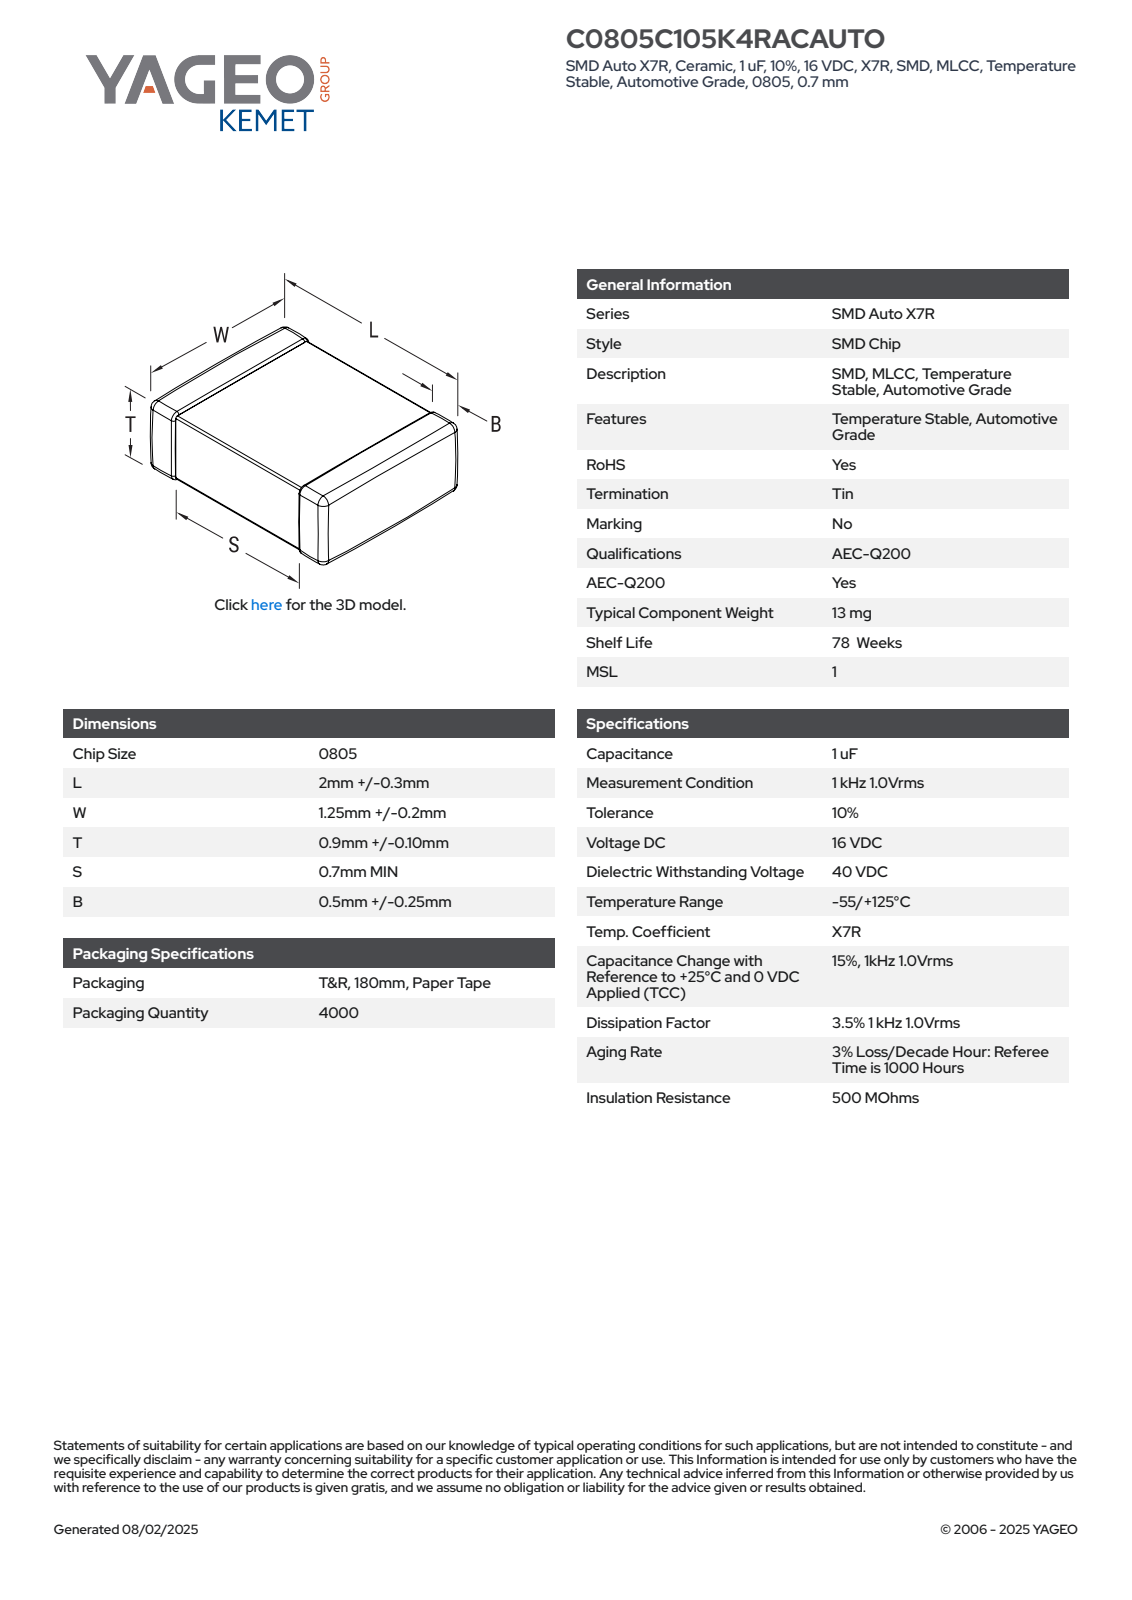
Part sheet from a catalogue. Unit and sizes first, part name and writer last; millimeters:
Units: millimetres
Overall size (bounding box): 2.3 × 1.45 × 1
Main face-to-face distances: 0.97, 1, 1.42, 2.3, 1.45, 0.94, 1.39, 1.03, 1.27, 1.24
Volume: 3 mm³ · Surface area: 14 mm²
Bodies: 4 solids, 125 faces (71 planar, 38 cylindrical, 16 other)
Part name (STEP PRODUCT): CCS_CCSTD_0805_L2.3W1.45T1B0.5
STEP written by: SolidWorks 2021 (AUTOMOTIVE_DESIGN)
